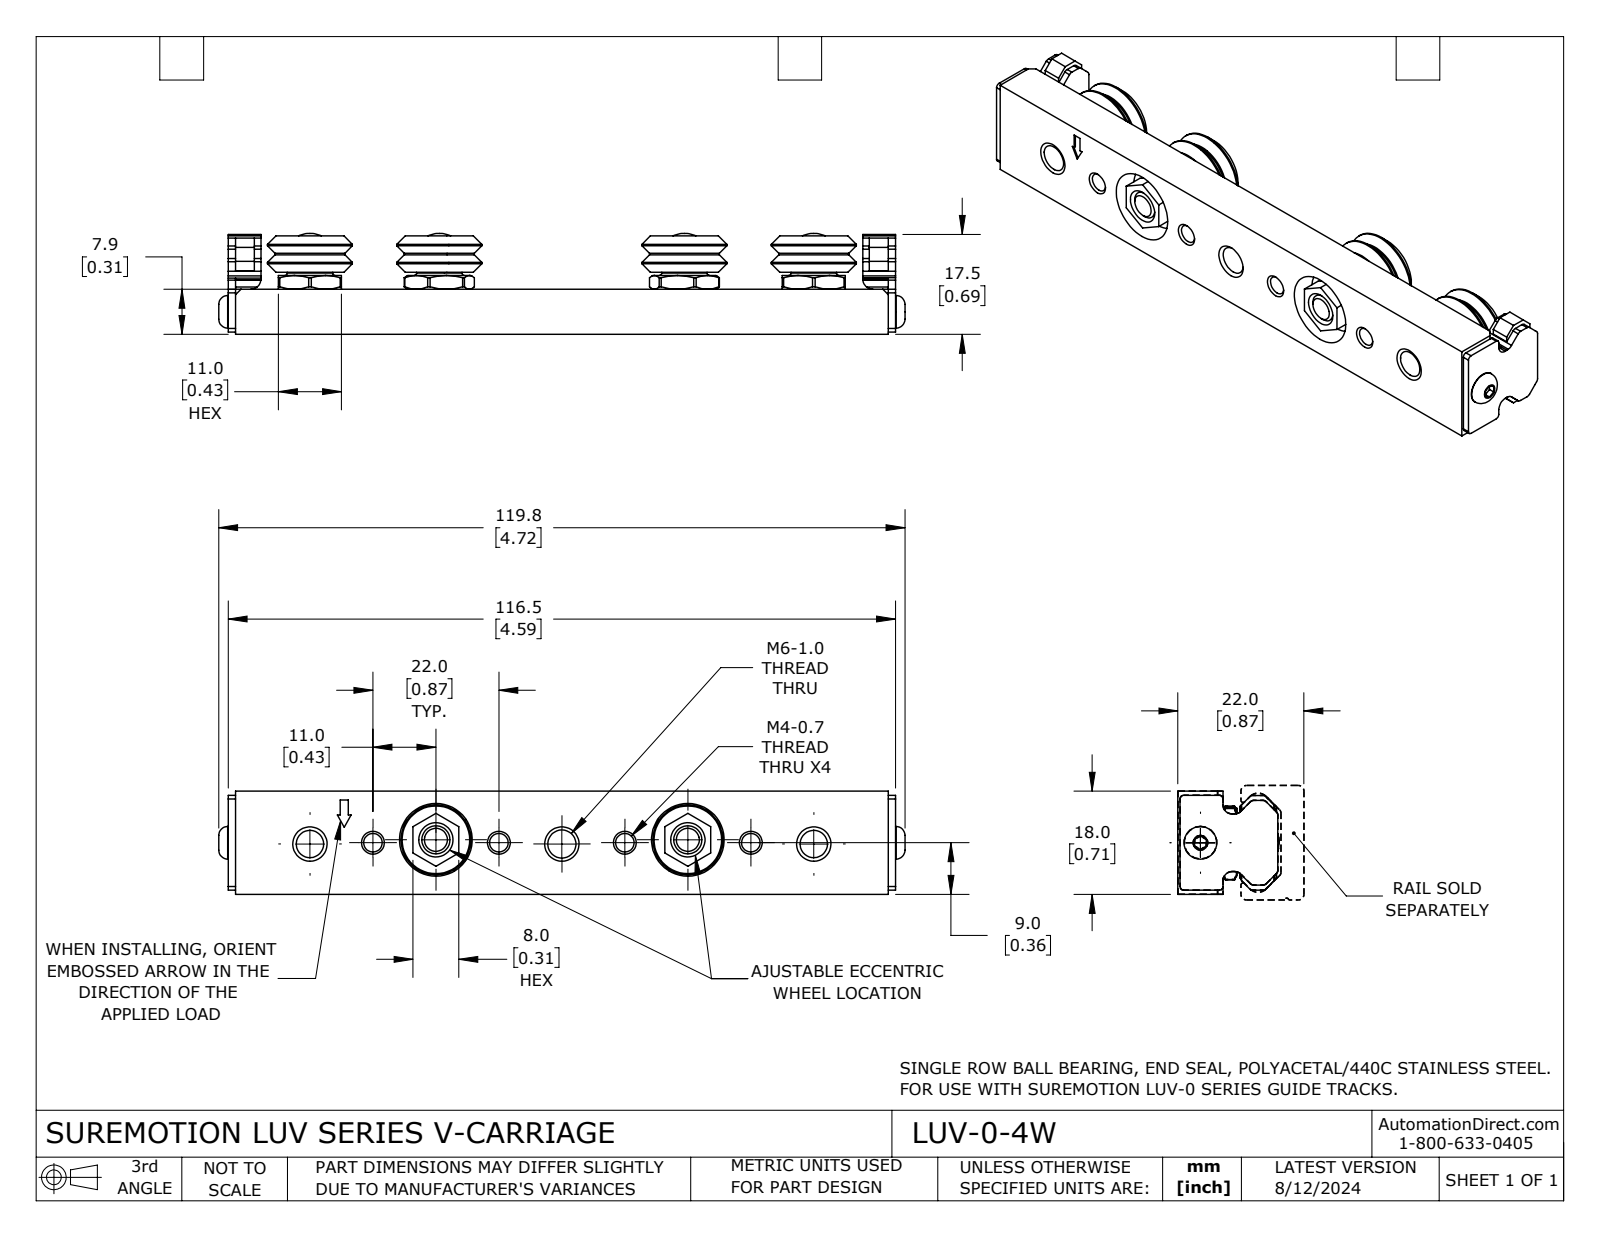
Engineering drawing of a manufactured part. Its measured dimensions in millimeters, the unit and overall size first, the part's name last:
Units: millimetres
Overall size (bounding box): 119.83 × 18.01 × 17.63
Round holes (diameter × count): ⌀3.24 ×4, ⌀4 ×4, ⌀4.92 ×4, ⌀9.18 ×4, ⌀9.44 ×4, ⌀5.63 ×2, ⌀12.7 ×2, ⌀2.46 ×1, ⌀4.92 ×1
Round bosses / shafts (diameter × count): ⌀14.83 ×4, ⌀7.92 ×4, ⌀6.22 ×4, ⌀3.99 ×4, ⌀11.81 ×2, ⌀6.48 ×2, ⌀6.48 ×2, ⌀6 ×2
Partial cylindrical surfaces — rounded edges, fillets, slot ends (radius × count): R0.38 ×12, R0.84 ×6, R0.64 ×4, R1.6 ×4, R6.22 ×4, R1.78 ×2
Main face-to-face distances: 7.87, 18, 1.27, 115.27, 6.35, 2.72, 5.15, 114, 2.97, 5.69
Hole centre spacings: 11, 32.99, 43.99, 54.99, 22, 0.62, 10.41, 11.01
Volume: 21 467 mm³ · Surface area: 14 307 mm²
Bodies: 9 solids, 842 faces (246 planar, 256 cylindrical, 340 other)
Part name (STEP PRODUCT): LUV-0-4W
STEP written by: SolidWorks 2023 (CONFIG_CONTROL_DESIGN)
